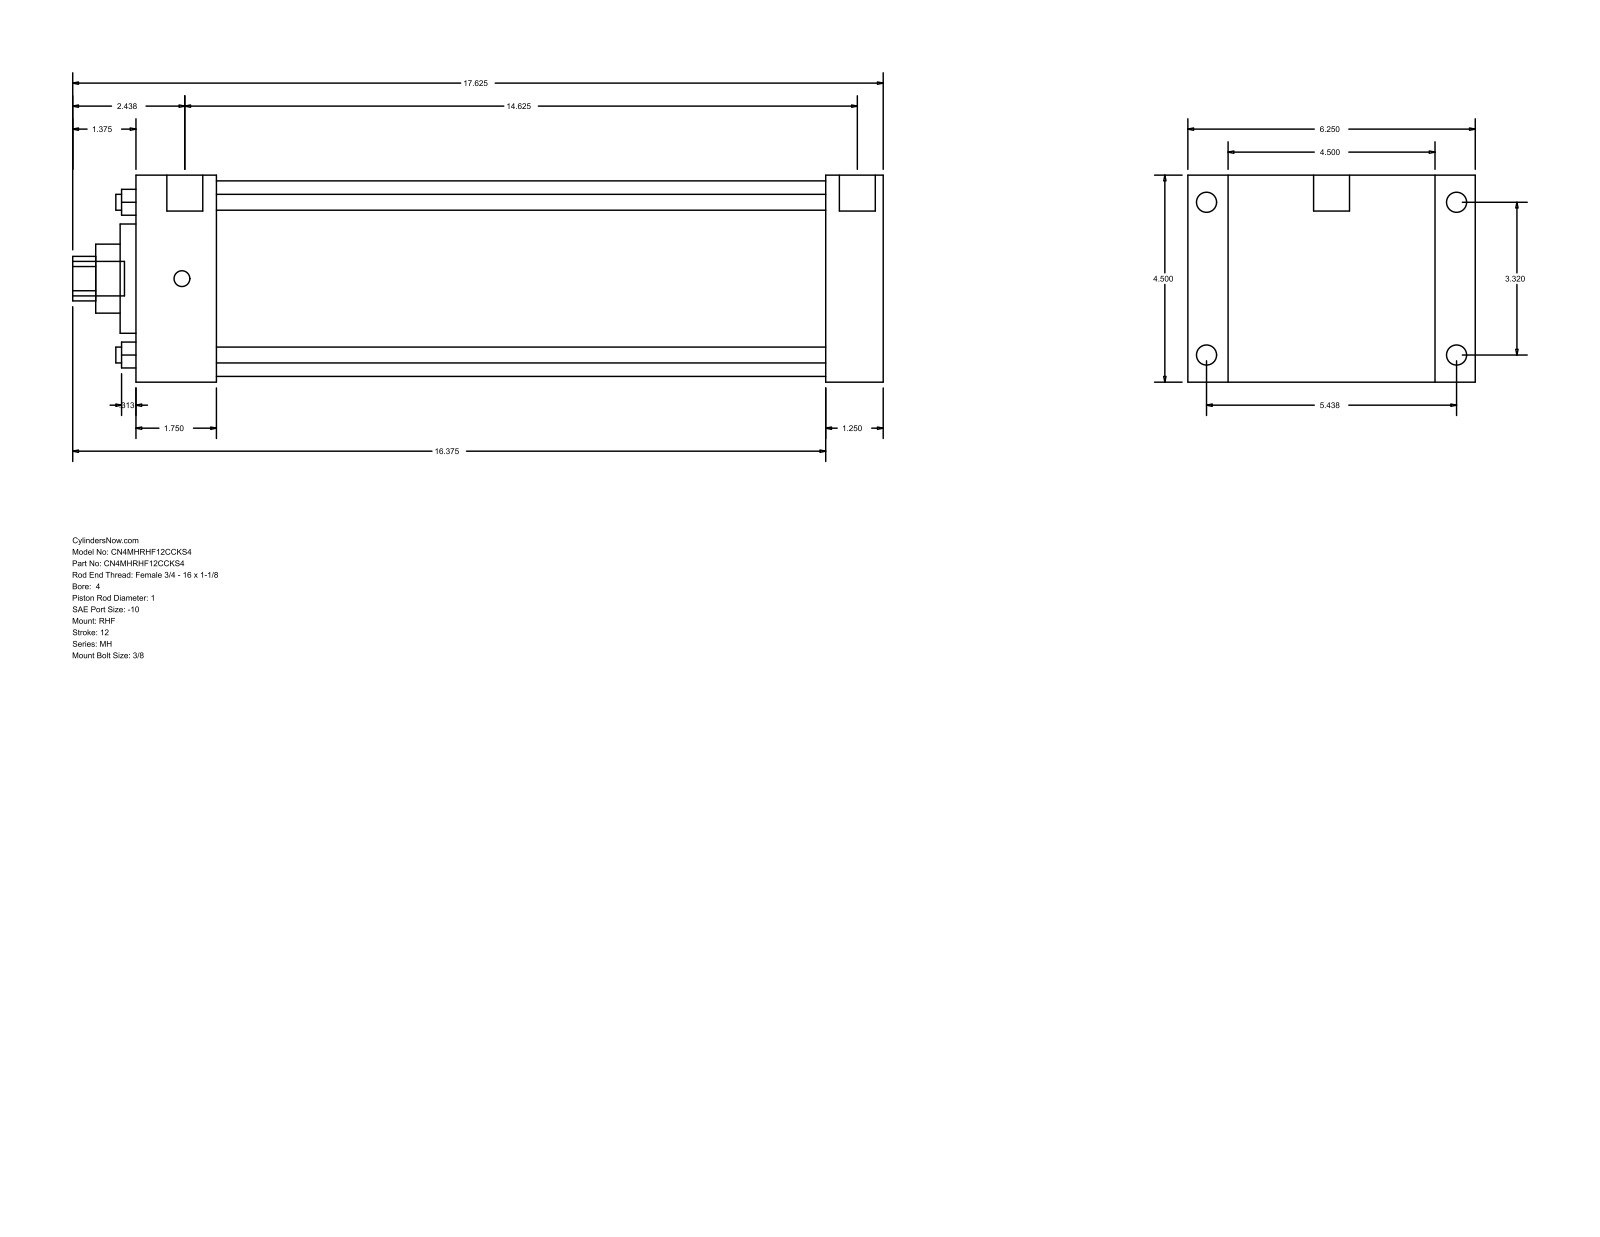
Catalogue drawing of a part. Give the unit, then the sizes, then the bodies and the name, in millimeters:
Units: millimetres
Overall size (bounding box): 447.68 × 158.75 × 114.3
Round holes (diameter × count): ⌀8.76 ×4, ⌀25.4 ×1, ⌀38.1 ×1, ⌀60.33 ×1, ⌀107.95 ×1
Round bosses / shafts (diameter × count): ⌀11.13 ×4, ⌀8.73 ×4, ⌀19.84 ×2, ⌀19.05 ×1
Partial cylindrical surfaces — rounded edges, fillets, slot ends (radius × count): R12.29 ×1
Main face-to-face distances: 114.3, 412.76, 381.01, 31.75, 22.23, 136.53, 44.46, 336.55, 368.3, 158.76
Hole centre spacings: 59.62, 84.32, 119.25
Bodies: 0 solids, 90 faces (61 planar, 29 cylindrical, 0 other)
Part name (STEP PRODUCT): MH_RHF__0400_1
STEP written by: GSSL Pune (CONFIG_CONTROL_DESIGN)
